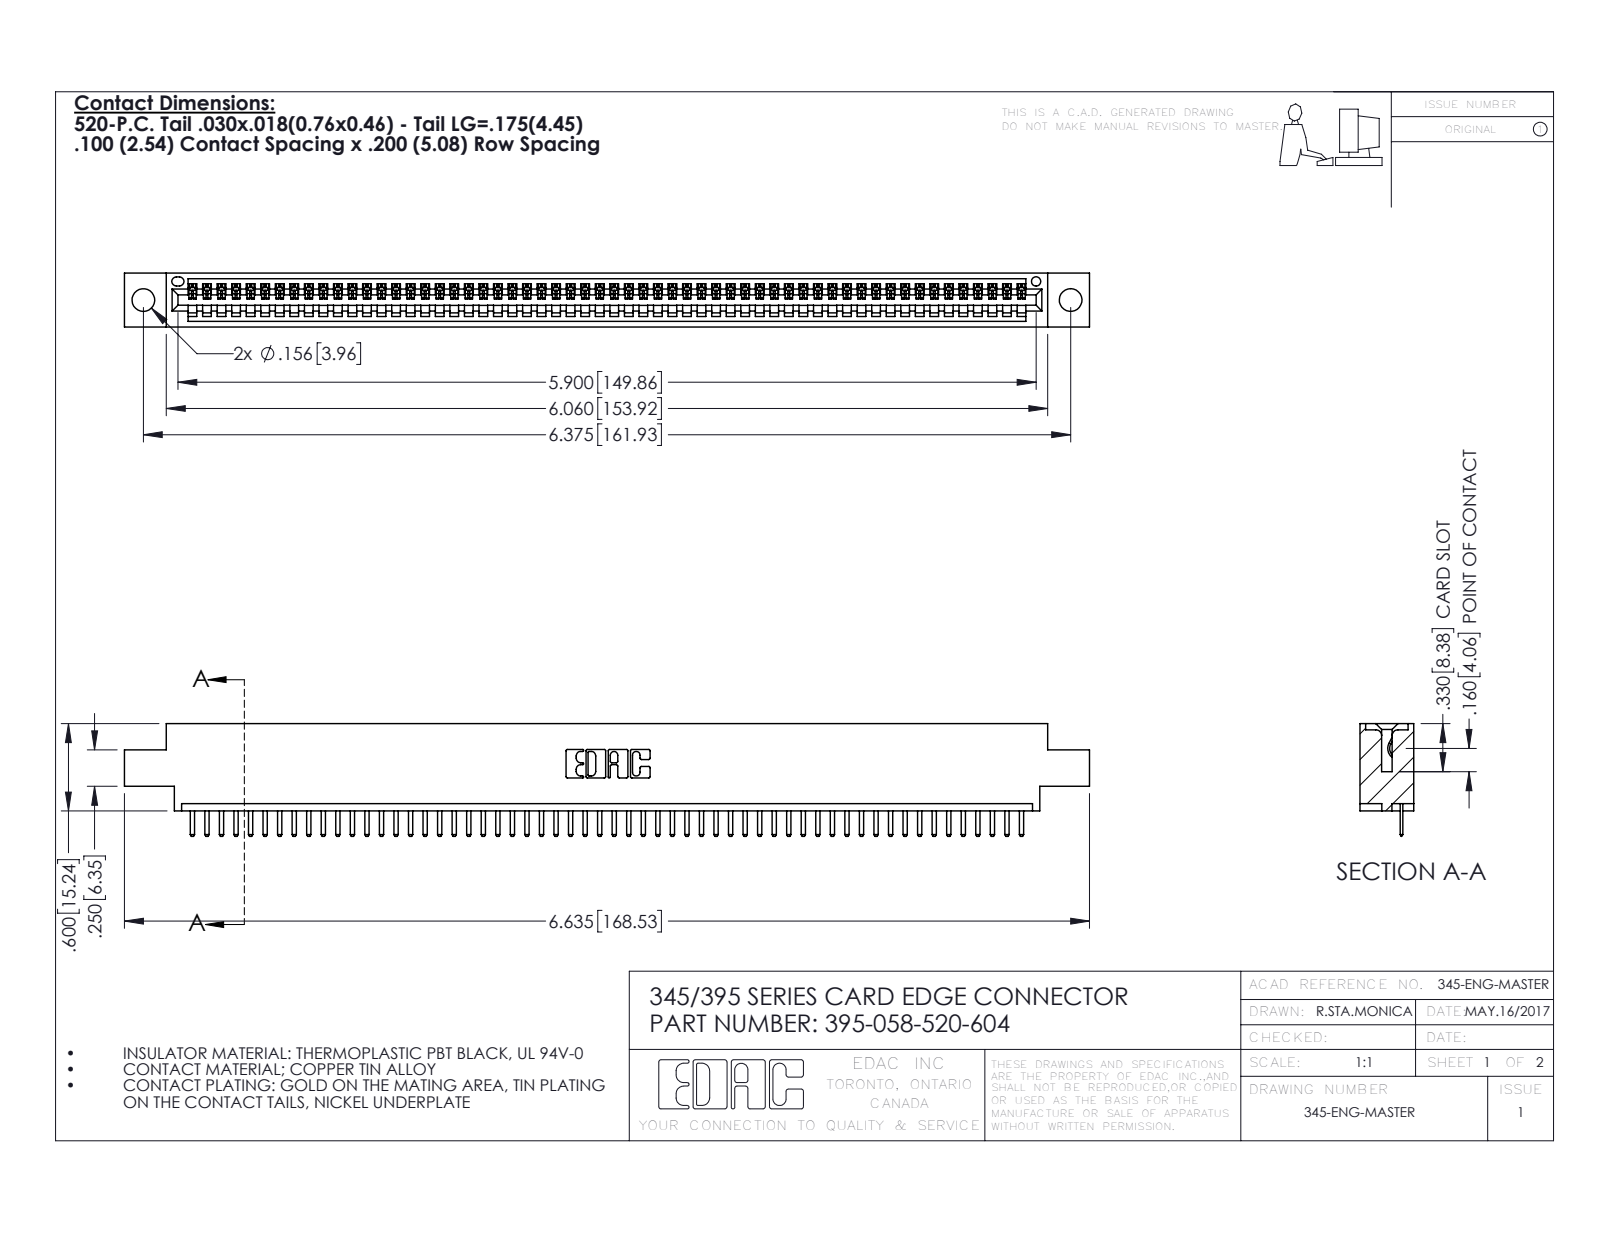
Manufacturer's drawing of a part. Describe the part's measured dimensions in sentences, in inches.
The part is named "345-292-001_345-293-120; 395-058-520-604; 345 Part_0.170 Offset - 0.156 Dia-TH". Its 3-D file was written by "SolidWorks 2016 (CONFIG_CONTROL_DESIGN)". It is 59 solids with 3726 faces: 2520 planar, 1206 cylindrical and 0 other. Overall it measures 6.635 by 0.775 by 0.37 inches. Its volume is 0.962 cubic inches and its surface area 31.87 square inches. Round holes: 2 of diameter 0.156, 1 of diameter 0.064. Partial cylindrical surfaces (rounded edges, fillets, slot ends): 118 of radius 0.01, 116 of radius 0.006, 22 of radius 0.01, 6 of radius 0.007, 6 of radius 0.031, 3 of radius 0.026, 2 of radius 0.031, 2 of radius 0.04. The main face-to-face distances are 0.298, 0.072, 0.37, 0.2, 0.098, 0.272, 0.025, 0.225, 0.072, 0.175. The hole center spacings are 0.27, 6.139, 6.375.
